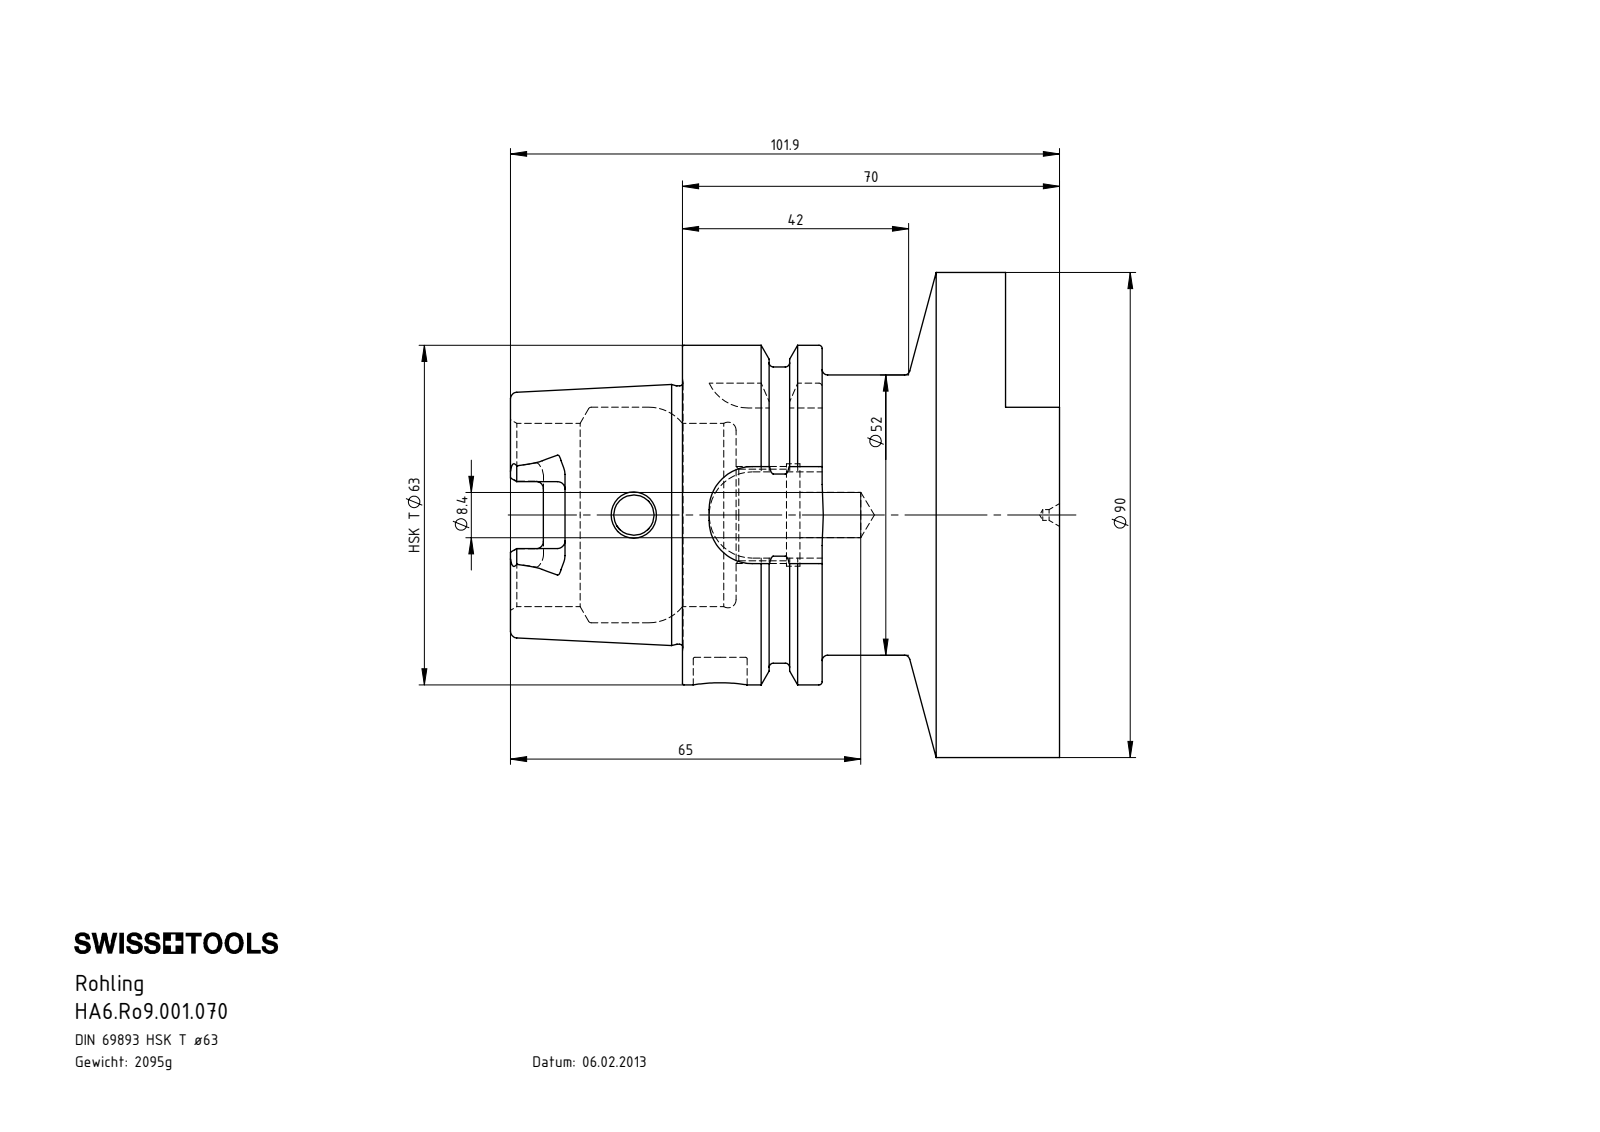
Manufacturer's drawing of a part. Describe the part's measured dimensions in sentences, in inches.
The part is named "HA6.Ro9.001.070". Its 3-D file was written by "SolidWorks 2017 (AUTOMOTIVE_DESIGN)". It is 1 solid with 121 faces: 43 planar, 33 cylindrical and 45 other. Overall it measures 4.012 by 3.543 by 3.543 inches. Its volume is 17.17 cubic inches and its surface area 62.27 square inches. Round holes: 1 of diameter 0.079, 1 of diameter 0.295, 1 of diameter 0.331, 1 of diameter 0.394, 1 of diameter 0.669, 1 of diameter 0.748, 1 of diameter 1.339, 1 of diameter 1.575. Round bosses or shafts: 1 of diameter 3.543, 1 of diameter 2.48, 1 of diameter 2.163, 1 of diameter 2.047, 1 of diameter 1.887. Partial cylindrical surfaces (rounded edges, fillets, slot ends): 6 of radius 0.055, 4 of radius 0.113, 4 of radius 0.315. The main face-to-face distances are 2.756, 1.022, 1.734, 0.63, 0.392, 2.364, 1.256, 1.648, 2.278, 4.012.
